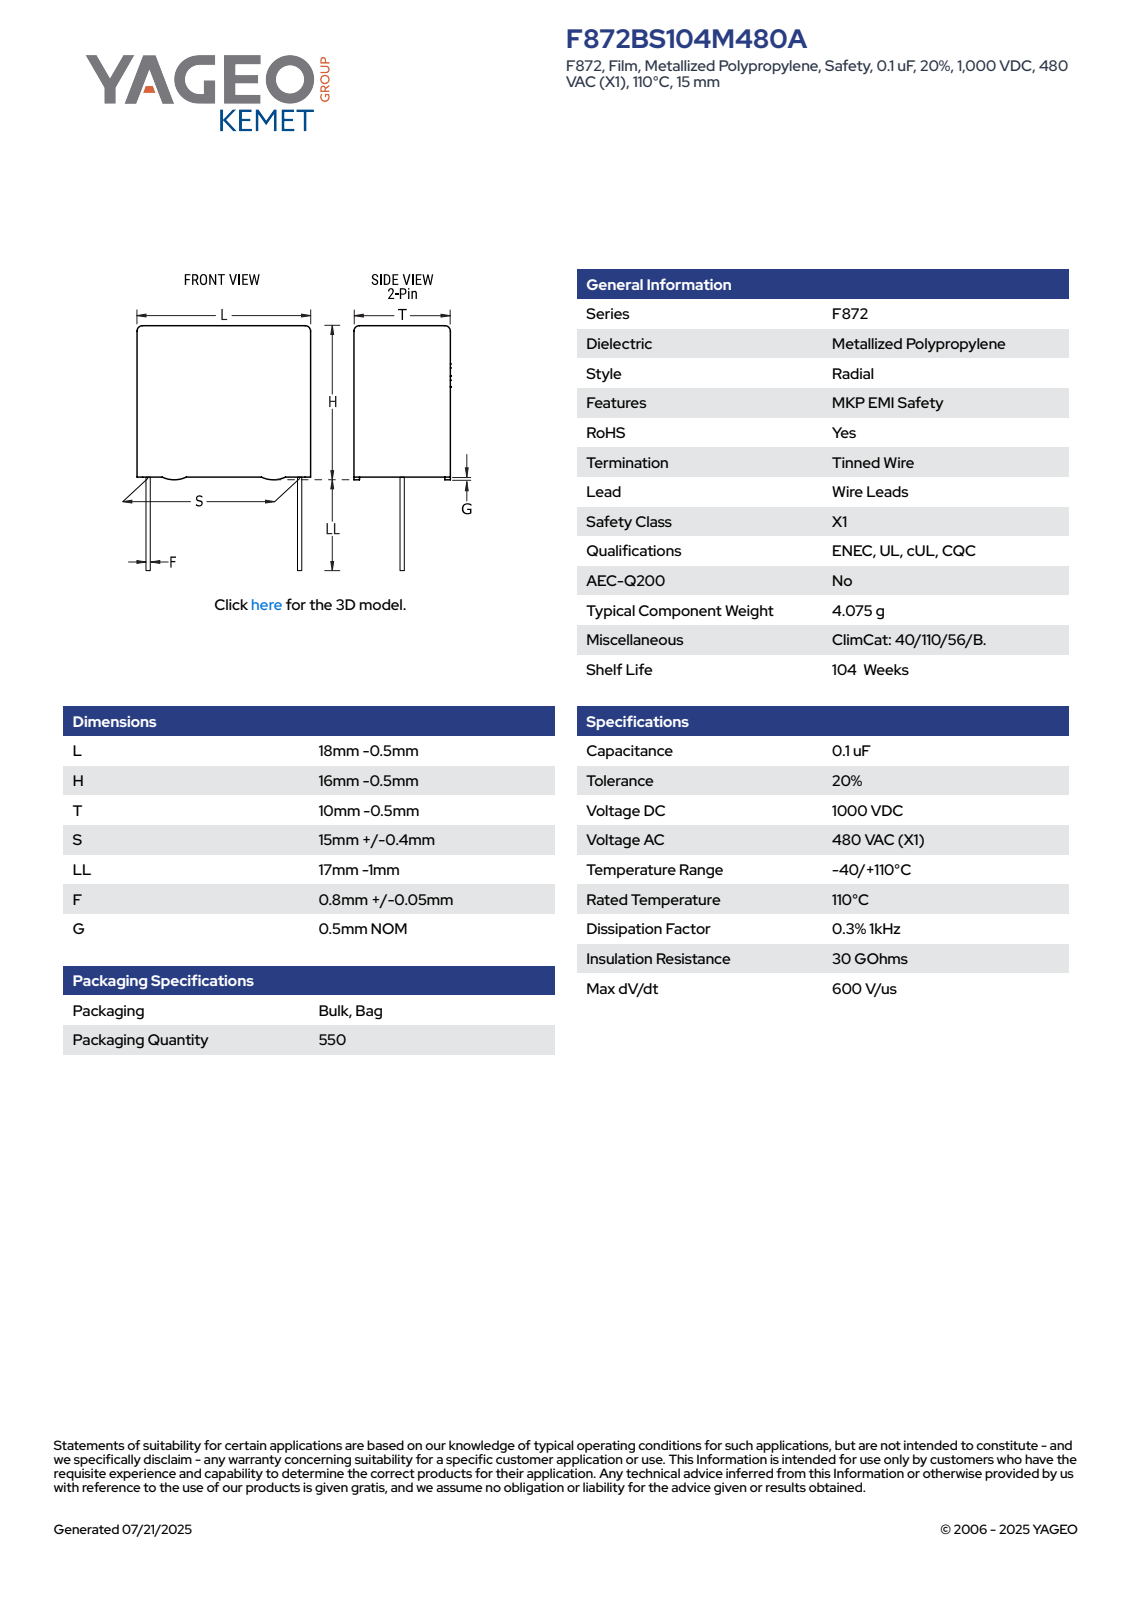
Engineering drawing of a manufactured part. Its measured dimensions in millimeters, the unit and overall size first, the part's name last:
Units: millimetres
Overall size (bounding box): 31.5 × 17.5 × 9.51
Round bosses / shafts (diameter × count): ⌀0.85 ×2
Partial cylindrical surfaces — rounded edges, fillets, slot ends (radius × count): R0.5 ×4
Main face-to-face distances: 9.5, 15, 17.5, 0.5, 15.5, 0.54, 8.96, 8.42, 16, 16.5
Volume: 2 513 mm³ · Surface area: 1 265 mm²
Bodies: 4 solids, 89 faces (81 planar, 8 cylindrical, 0 other)
Part name (STEP PRODUCT): CFR_RBG_18X16X10_L17.5H15.5T9.5S15LL16F0.85G0.5
STEP written by: SolidWorks 2014 (AUTOMOTIVE_DESIGN)
